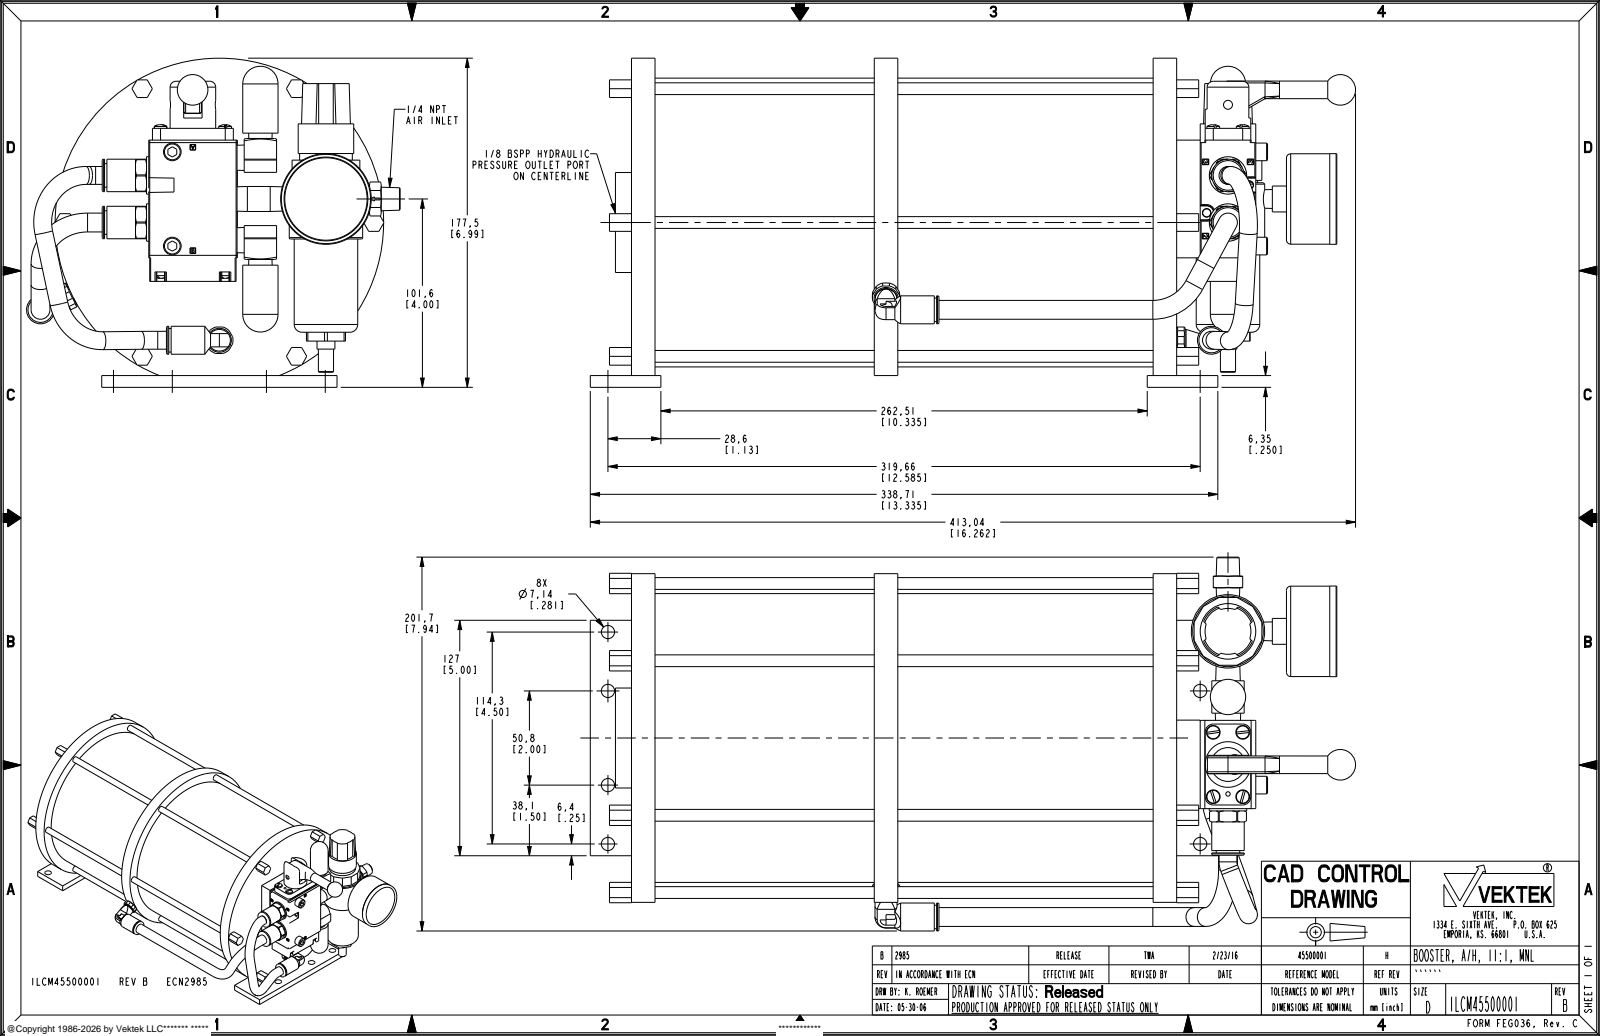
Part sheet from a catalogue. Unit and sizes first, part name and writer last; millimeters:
Units: millimetres
Overall size (bounding box): 413.04 × 201.66 × 177.55
Round holes (diameter × count): ⌀7.14 ×12, ⌀5.11 ×4, ⌀12.7 ×3, ⌀5.41 ×2, ⌀6.65 ×2, ⌀13.72 ×2, ⌀17.53 ×2, ⌀20.17 ×2, ⌀2.38 ×1, ⌀2.5 ×1, ⌀3.68 ×1, ⌀4.83 ×1
Round bosses / shafts (diameter × count): ⌀6.35 ×12, ⌀9.65 ×6, ⌀10.16 ×4, ⌀9.53 ×4, ⌀6.9 ×4, ⌀11.68 ×3, ⌀15.09 ×2, ⌀12.7 ×2
Partial cylindrical surfaces — rounded edges, fillets, slot ends (radius × count): R1 ×19, R0.5 ×16, R1.52 ×6, R0.51 ×4, R3.3 ×4, R3.7 ×4, R4.37 ×4, R5.96 ×4
Main face-to-face distances: 294.26, 12.7, 281.56, 131.04, 150.52, 6.35, 163.22, 143.74, 118.34, 268.86
Hole centre spacings: 50.8, 19.05, 31.75, 37.03, 54.25, 82.55, 84.72, 300.61
Volume: 5 982 000 mm³ · Surface area: 376 619 mm²
Bodies: 1 solid, 1189 faces (552 planar, 330 cylindrical, 307 other)
Part name (STEP PRODUCT): ILCM45500001
STEP written by: PRO/ENGINEER BY PARAMETRIC TECHNOLOGY CORPORATION, 2013320 (CONFIG_CONTROL_DESIGN)
